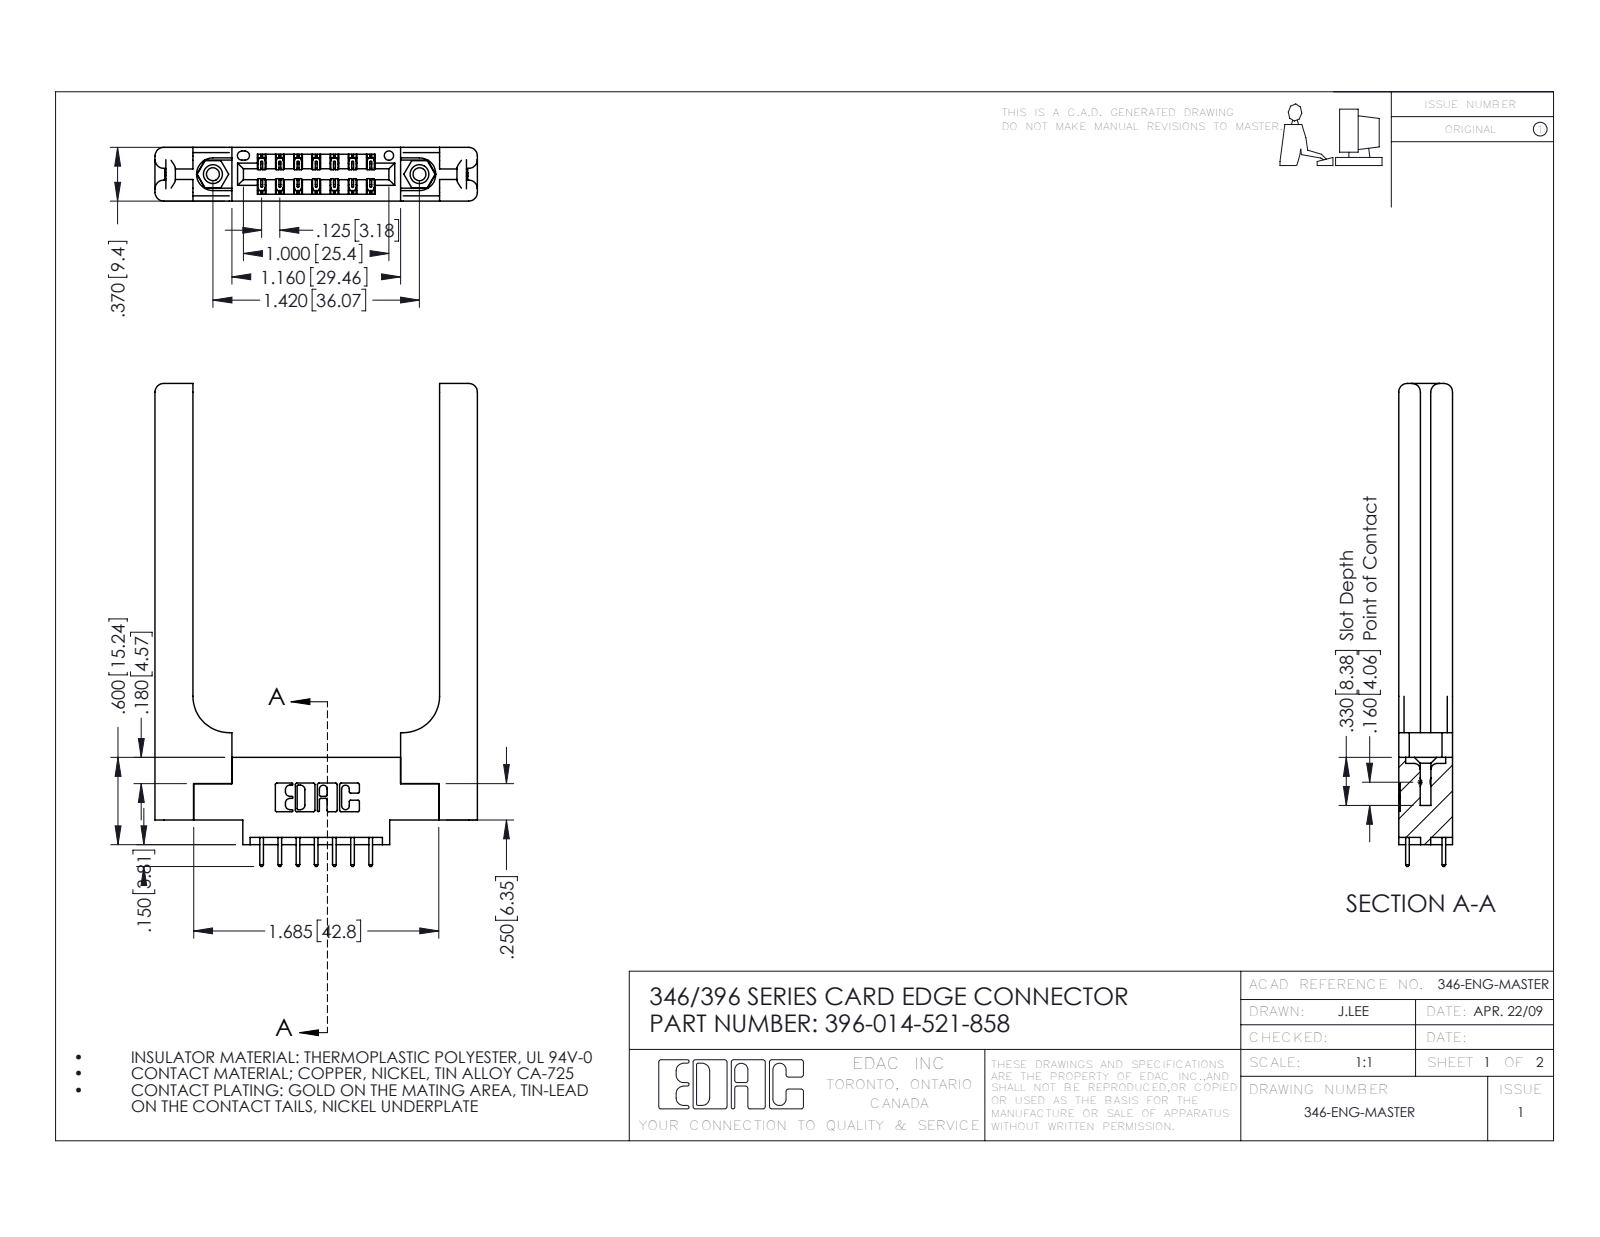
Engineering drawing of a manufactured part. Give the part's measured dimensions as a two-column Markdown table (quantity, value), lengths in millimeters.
| quantity | value |
| --- | --- |
| part name | 396-014-521-858; 346-220-058_345-220-058; 345-292-001_345-293-121; 345-250-001_345-250-001-102 (+1 more) |
| STEP written by | SolidWorks 2016 (CONFIG_CONTROL_DESIGN) |
| units | millimeters |
| bodies | 19 solids, 1110 faces (718 planar, 332 cylindrical, 60 other) |
| overall size | 84.3 × 56.3 × 9.4 |
| volume | 12 600 mm³ |
| surface area | 11 520 mm² |
| round holes (diameter × count) | 2.3 × 2, 3.2 × 2, 4 × 2, 1.6 × 1 |
| round bosses / shafts (diameter × count) | 3.9 × 2 |
| partial cylindrical surfaces (radius × count) | 0.3 × 22, 0.2 × 21, 1.5 × 16, 0.3 × 14, 0.2 × 6, 0.8 × 6, 0.7 × 3, 0.4 × 2 |
| main face-to-face distances | 9.4, 3.8, 5.6, 1.8, 3.8, 6.4, 2.6, 1.2, 8.2, 4.4 |
| hole center spacings | 6.2, 30.9, 36.1 |
